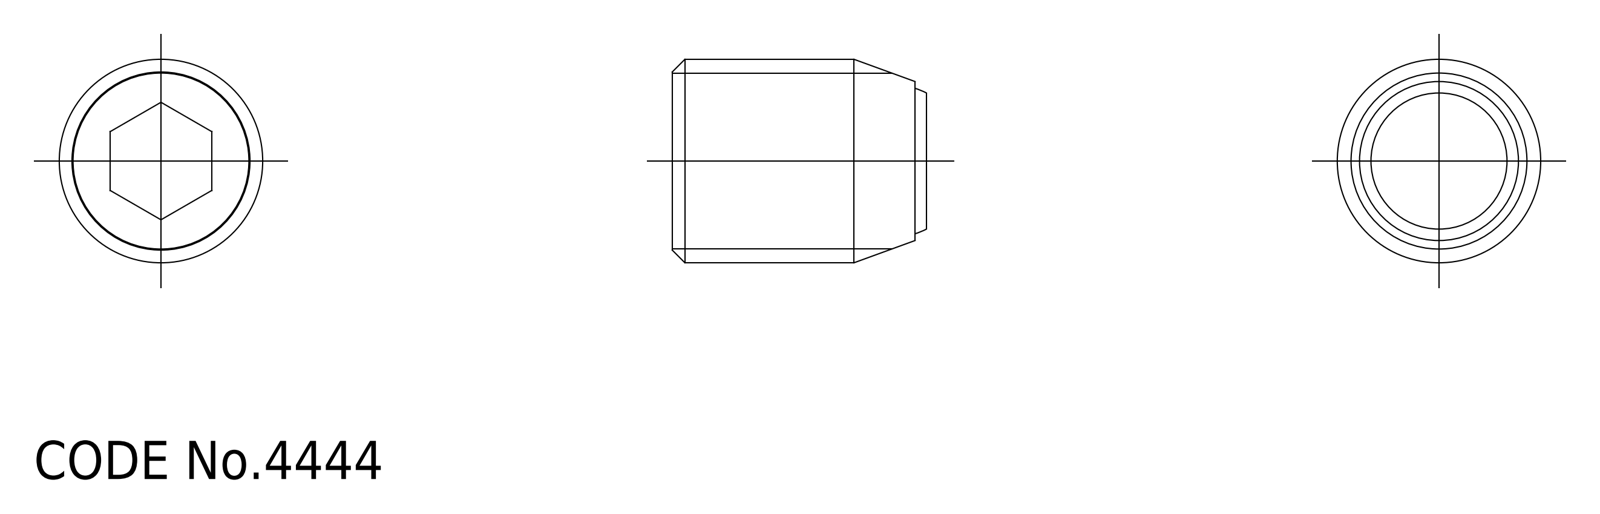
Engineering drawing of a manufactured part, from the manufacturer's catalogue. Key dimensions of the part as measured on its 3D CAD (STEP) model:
Part name (STEP PRODUCT): ball; SCS_M16_20_F_16454_36
STEP written by: CADfix (AUTOMOTIVE_DESIGN)
Units: millimetres
Bodies: 2 solids, 20 faces (0 planar, 0 cylindrical, 20 other)
Overall size (bounding box): 21.38 × 16 × 16
Volume: 2 880 mm³ · Surface area: 2 235 mm²
